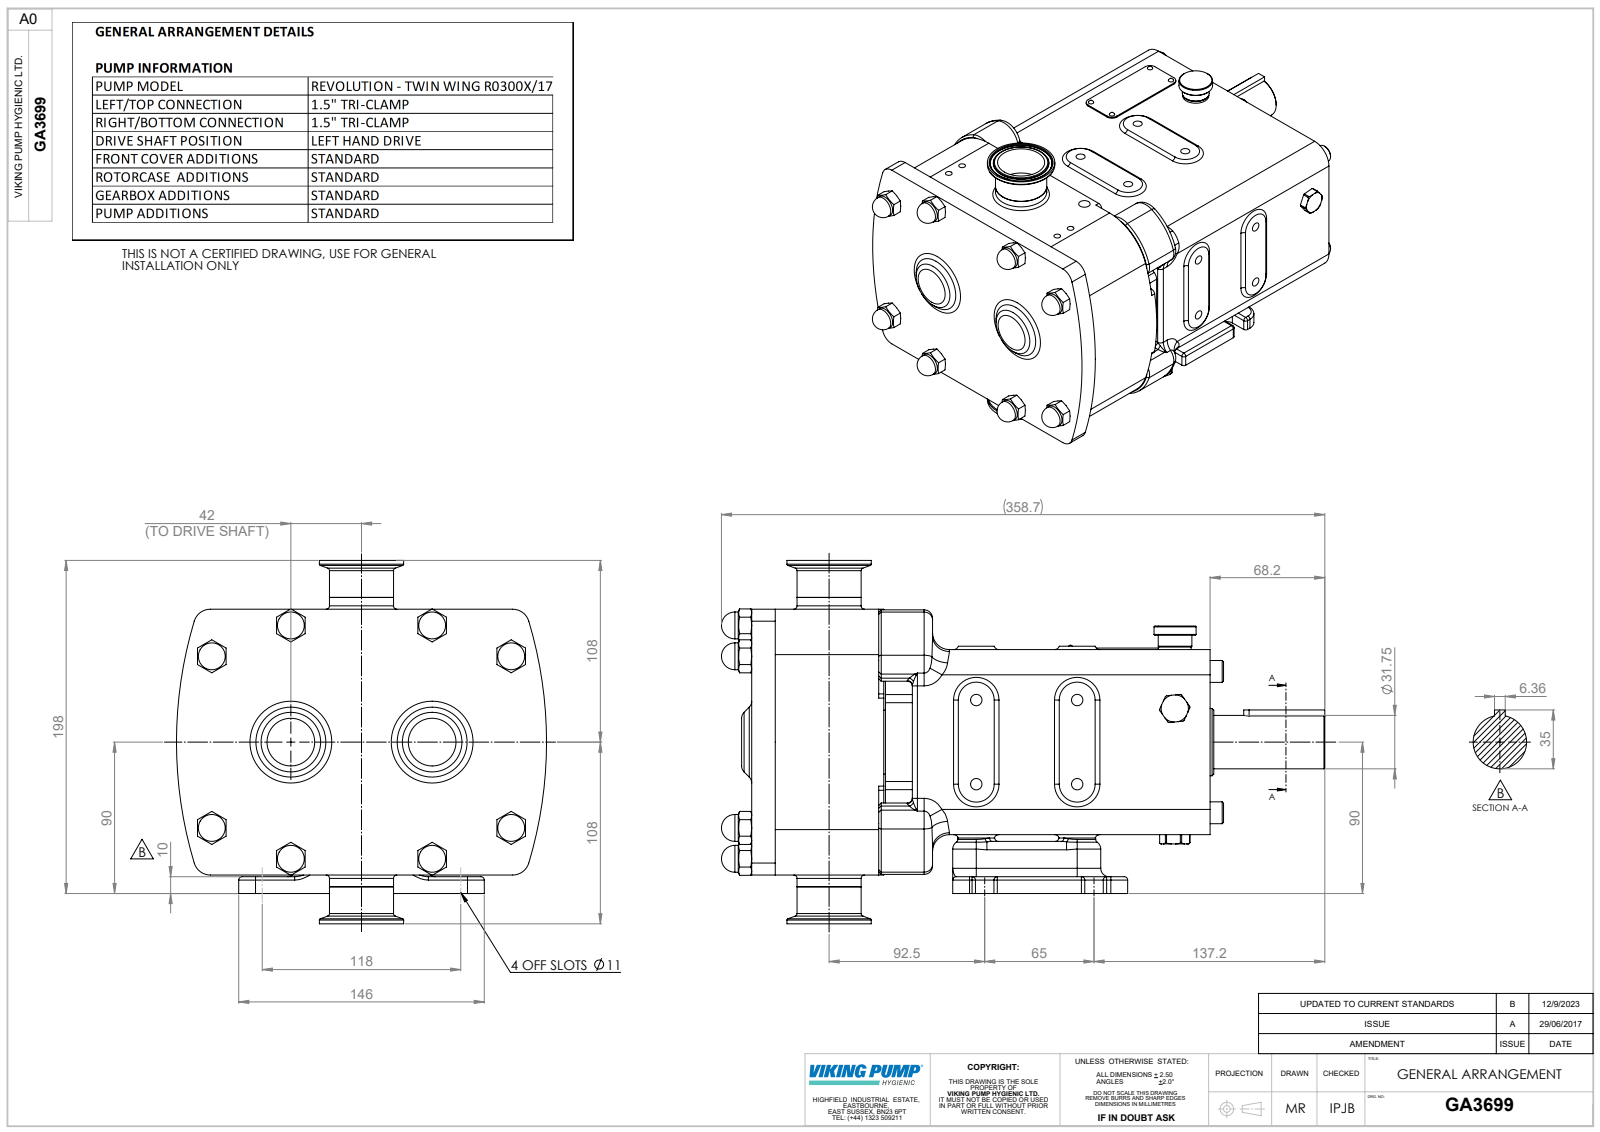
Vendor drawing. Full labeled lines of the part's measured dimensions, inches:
Part name (STEP PRODUCT): Copy of R0300 CPP V LHD^GA3699; Copy of RA94-5121-22M^GA3699; GA3699
STEP written by: SolidWorks 2023 (AUTOMOTIVE_DESIGN)
Units: inches
Bodies: 3 solids, 958 faces (293 planar, 297 cylindrical, 368 other)
Overall size (bounding box): 14.122 × 8.661 × 8.504
Volume: 426.6 in³ · Surface area: 566.7 in²
Round holes (diameter × count): ⌀0.268 ×8, ⌀0.197 ×4, ⌀0.337 ×2, ⌀0.906 ×1, ⌀1.38 ×1
Round bosses / shafts (diameter × count): ⌀0.63 ×8, ⌀0.512 ×7, ⌀1.972 ×1, ⌀1.575 ×1, ⌀1.5 ×1, ⌀1.496 ×1, ⌀1.25 ×1, ⌀0.984 ×1
Partial cylindrical surfaces — rounded edges, fillets, slot ends (radius × count): R0.394 ×30, R0.118 ×28, R0.079 ×24, R0.197 ×19, R0.232 ×8, R0.591 ×8, R0.217 ×4, R0.315 ×4
Main face-to-face distances: 7.638, 0.945, 0.039, 4.331, 3.091, 10.728, 5.276, 7.598, 3.13, 5.709
Hole centre spacings: 1.969, 2.362, 3.075, 0.551, 1.304, 1.812, 1.915, 2.253
